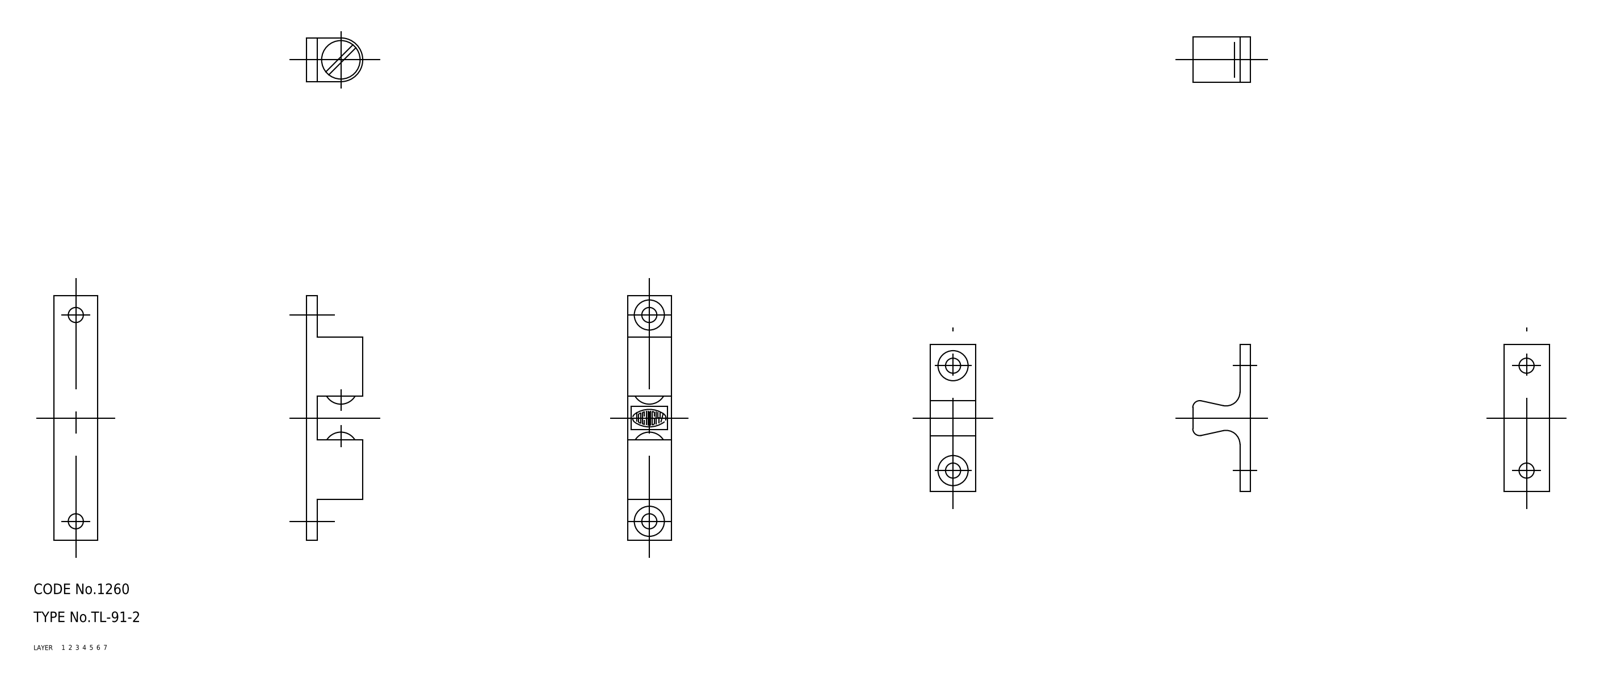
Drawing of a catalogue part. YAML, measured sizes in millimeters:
part_name: "screw; ball; keeper; housing (+1 more)"
step_written_by: "CADfix (AUTOMOTIVE_DESIGN)"
units: millimeters
bodies: {solids: 6, faces: 84, planar: 0, cylindrical: 0, other: 84}
overall_size: [70, 67.23, 13]
volume: 9409
surface_area: 7526
